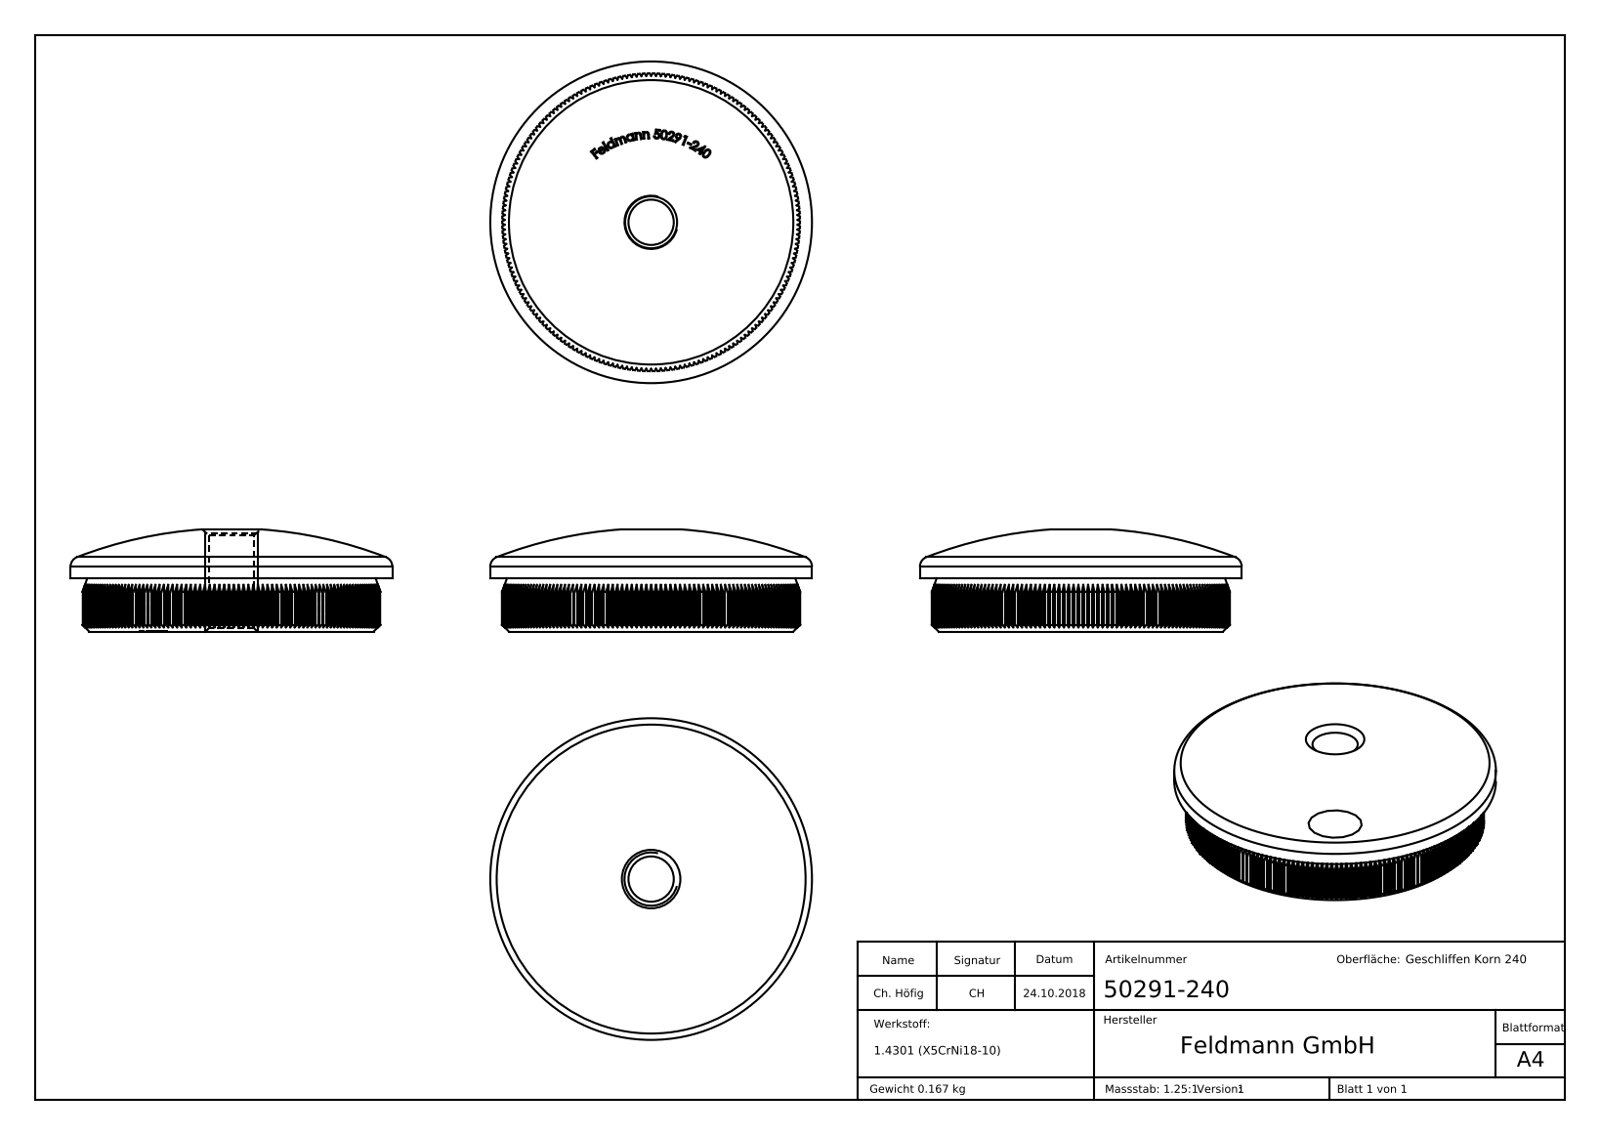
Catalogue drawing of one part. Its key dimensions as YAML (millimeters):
part_name: "50291-240"
step_written_by: "SolidWorks 2015 (CONFIG_CONTROL_DESIGN)"
units: millimeters
bodies: {solids: 1, faces: 813, planar: 512, cylindrical: 194, other: 107}
overall_size: [48.3, 48.3, 15.35]
volume: 21201
surface_area: 5944
round_holes:
  - {diameter: 6.8, count: 1}
round_bosses_or_shafts:
  - {diameter: 48.3, count: 1}
partial_cylinders:
  - {radius: 22.35, count: 1}
face_to_face_distances: [8, 22, 21.98, 22.02, 7.9, 0.66, 0.54, 0.67, 0.79, 0.72]
